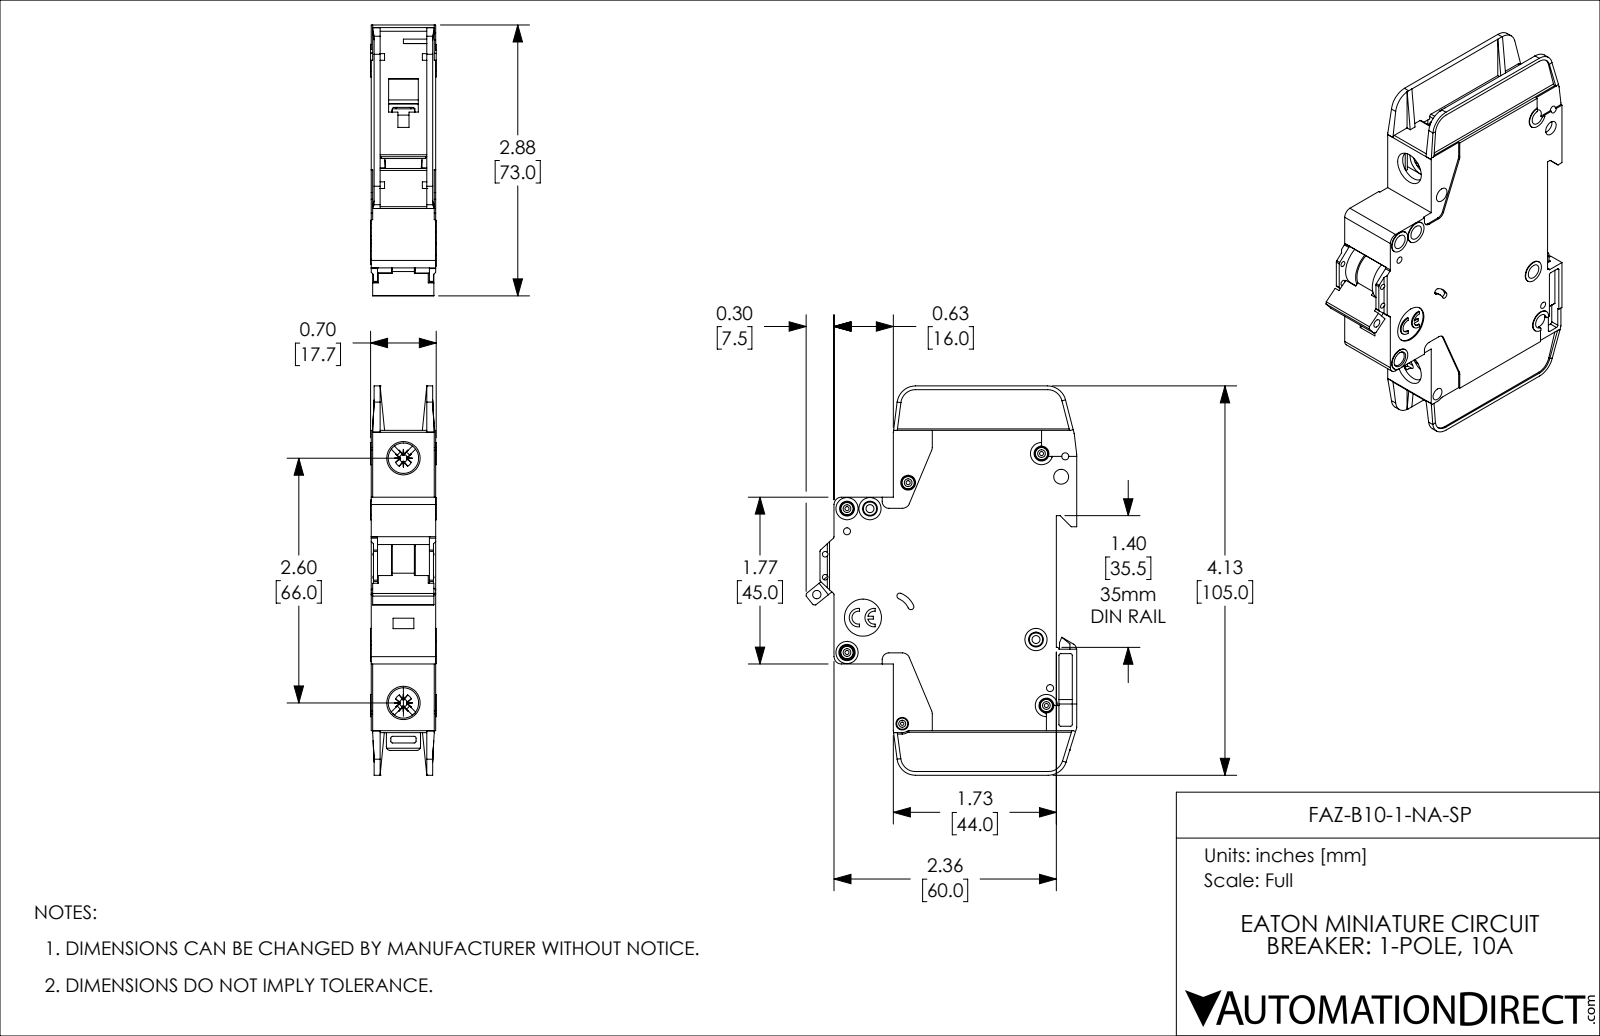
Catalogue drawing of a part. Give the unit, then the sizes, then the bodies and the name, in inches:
Units: inches
Overall size (bounding box): 4.134 × 2.876 × 0.697
Round holes (diameter × count): ⌀0.157 ×8, ⌀0.043 ×5, ⌀0.075 ×4, ⌀0.059 ×2, ⌀0.085 ×2, ⌀0.323 ×2, ⌀0.035 ×1, ⌀0.089 ×1, ⌀0.098 ×1, ⌀0.134 ×1, ⌀0.394 ×1
Round bosses / shafts (diameter × count): ⌀0.13 ×5, ⌀0.236 ×4, ⌀0.118 ×2, ⌀0.098 ×1
Partial cylindrical surfaces — rounded edges, fillets, slot ends (radius × count): R0.02 ×42, R0.016 ×10, R0.039 ×10, R0.079 ×8, R0.197 ×5, R0.008 ×4, R0.026 ×4, R0.043 ×4
Main face-to-face distances: 0.047, 0.685, 0.591, 0.638, 0.094, 0.543, 0.016, 0.031, 0.496, 0.575
Hole centre spacings: 0.244, 0.537, 0.87, 0.189, 0.199, 0.204, 0.221, 0.24
Volume: 4.682 in³ · Surface area: 41.01 in²
Bodies: 1 solid, 1127 faces (671 planar, 357 cylindrical, 99 other)
Part name (STEP PRODUCT): FAZ-B10-1-NA-SP
STEP written by: SolidWorks 2019 (AUTOMOTIVE_DESIGN)
